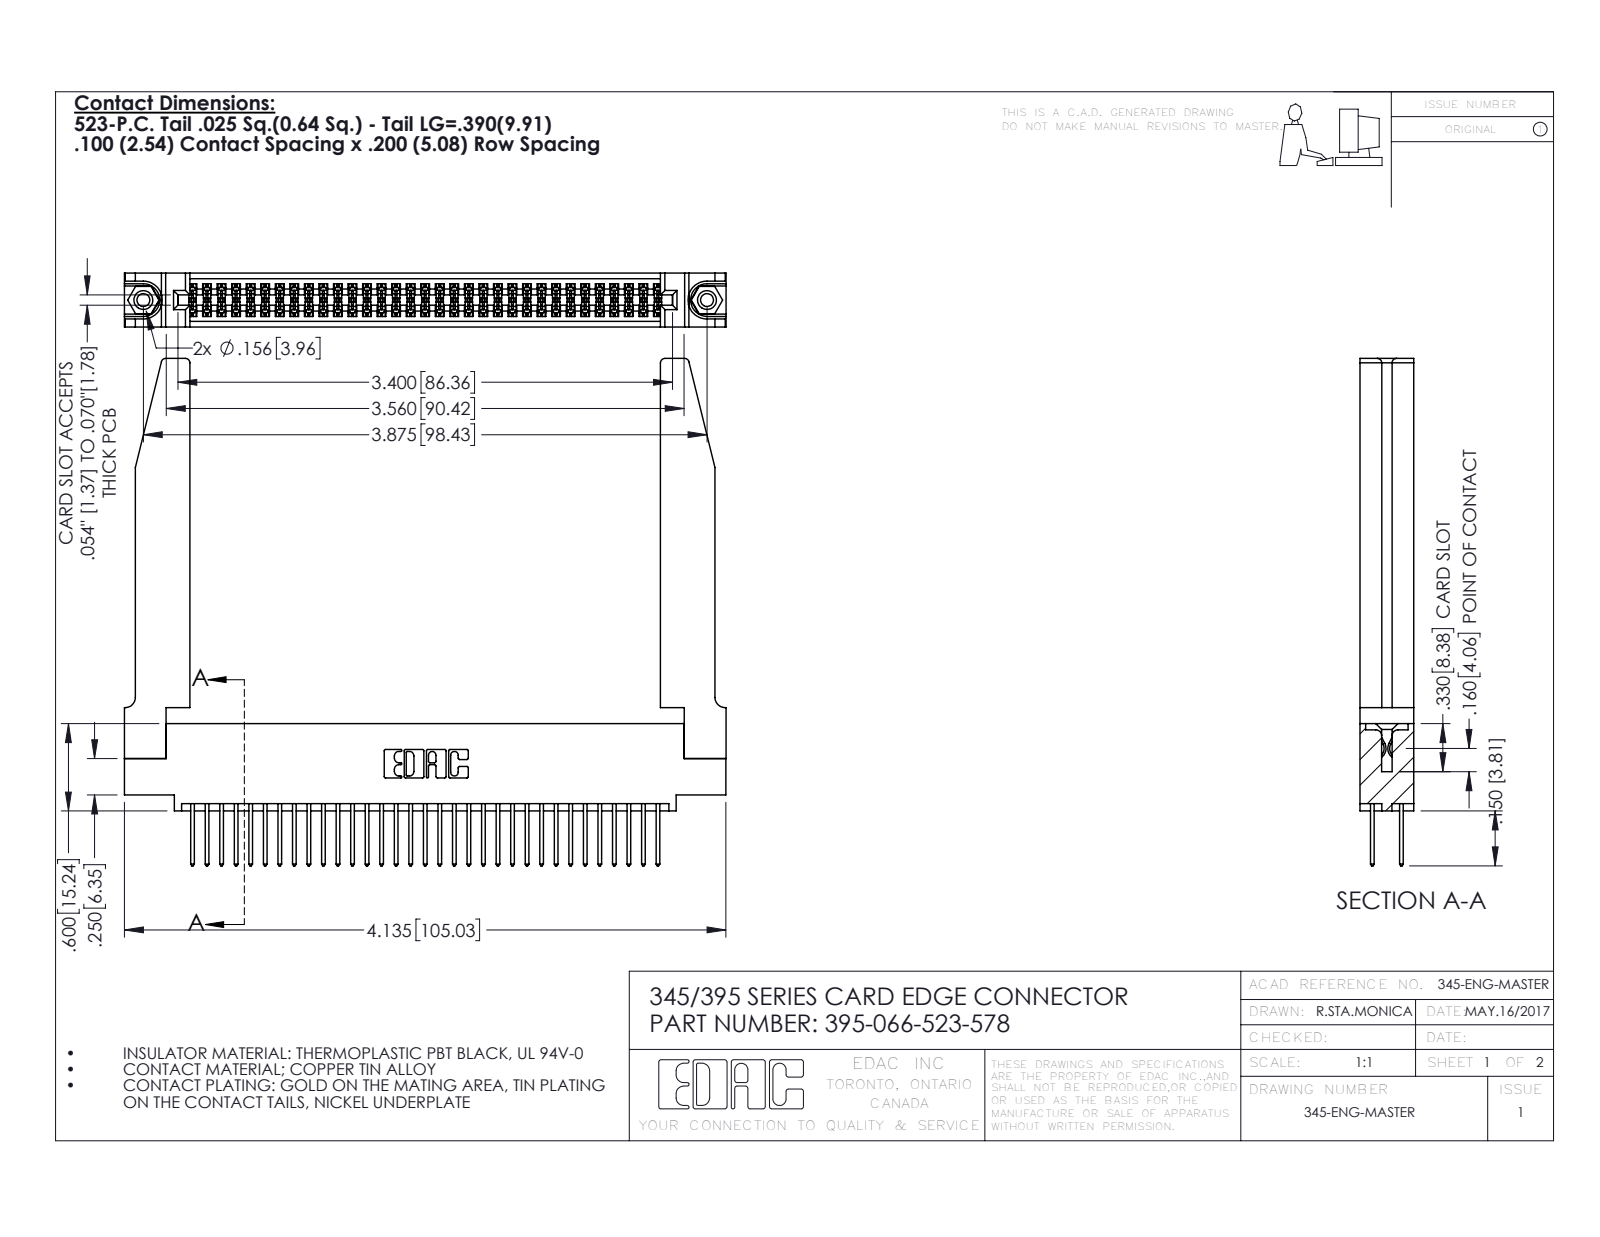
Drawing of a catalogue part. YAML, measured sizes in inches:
part_name: "345-292-001_345-293-123; 345 Part_0.110 Offset - 0.156 Dia-TH; 345-250-001_345-250-001-102; 345-220-078_345-220-078 (+1 more)"
step_written_by: "SolidWorks 2016 (CONFIG_CONTROL_DESIGN)"
units: inches
bodies: {solids: 71, faces: 3664, planar: 2404, cylindrical: 1208, other: 52}
overall_size: [4.136, 3.487, 0.37]
volume: 1.096
surface_area: 34.75
round_holes:
  - {diameter: 0.089, count: 2}
  - {diameter: 0.125, count: 2}
  - {diameter: 0.156, count: 2}
  - {diameter: 0.064, count: 1}
round_bosses_or_shafts:
  - {diameter: 0.155, count: 2}
partial_cylinders:
  - {radius: 0.006, count: 99}
  - {radius: 0.01, count: 66}
  - {radius: 0.01, count: 22}
  - {radius: 0.03, count: 8}
  - {radius: 0.007, count: 6}
  - {radius: 0.031, count: 6}
  - {radius: 0.026, count: 3}
  - {radius: 0.014, count: 2}
face_to_face_distances: [0.072, 0.37, 0.298, 0.2, 0.098, 0.272, 0.025, 0.225, 0.175, 0.148]
hole_center_spacings: [0.27, 3.64, 3.875]
